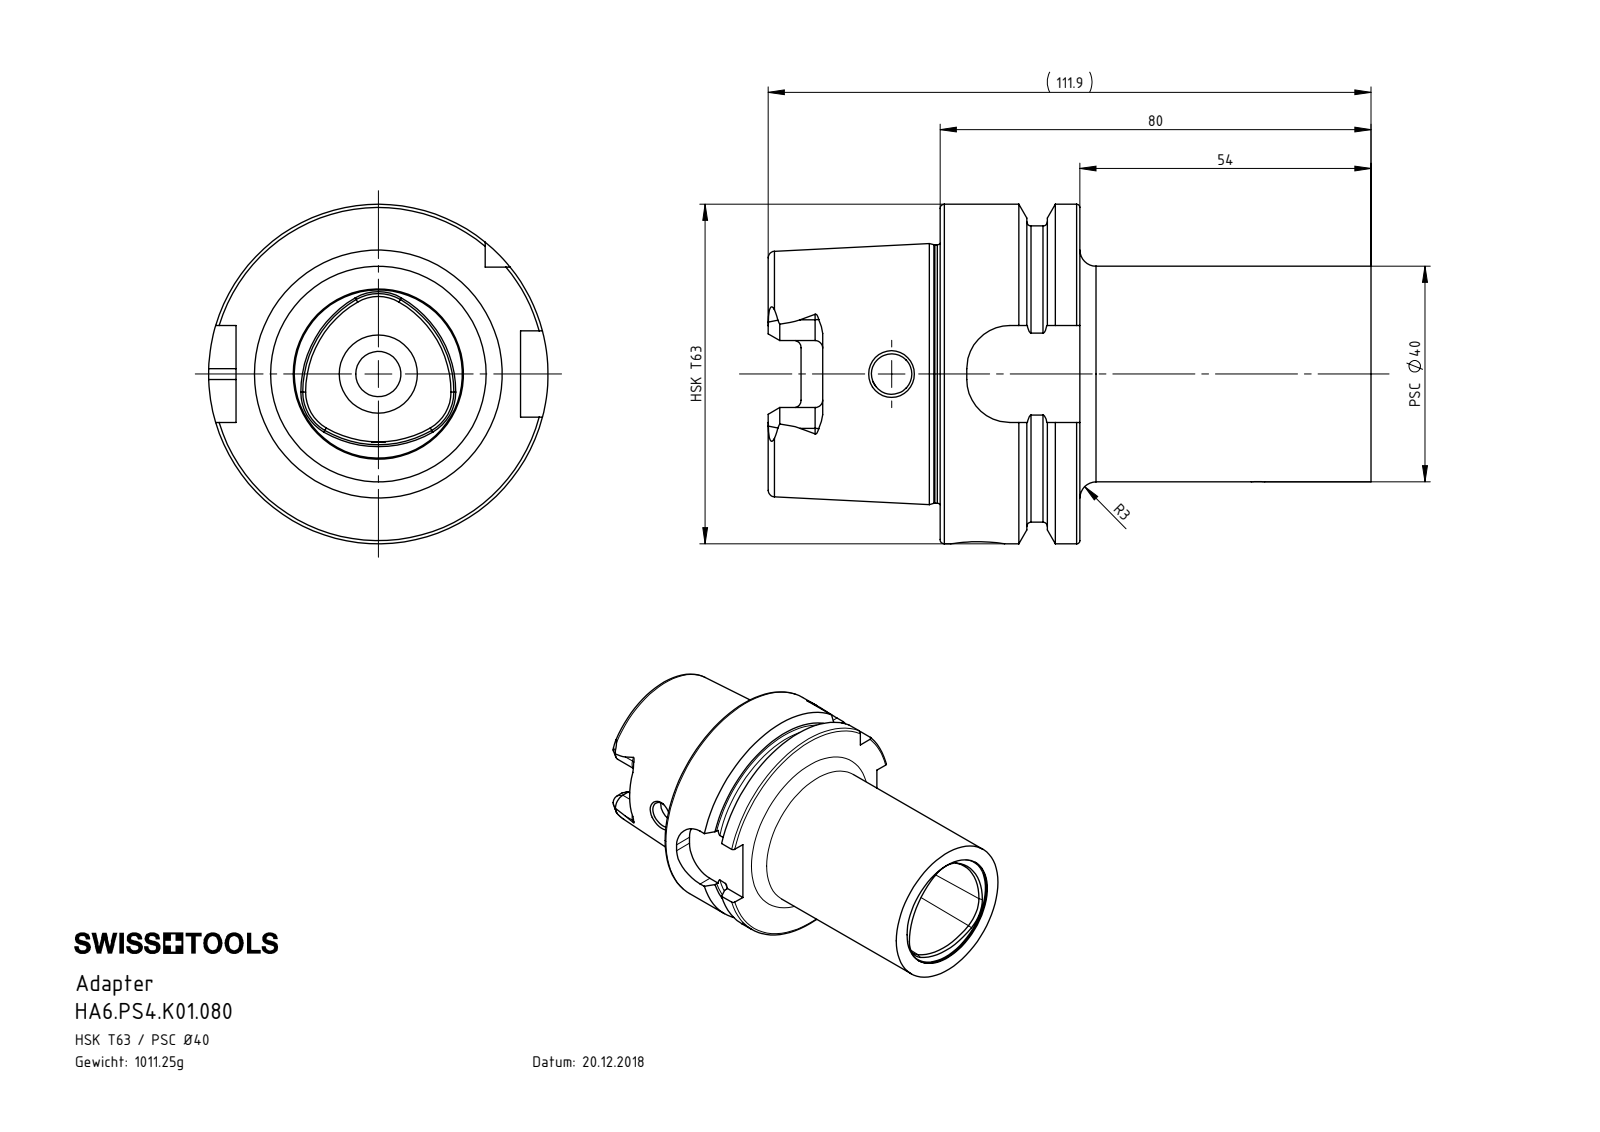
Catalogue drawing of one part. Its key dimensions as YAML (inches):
part_name: "HA6.PS4.K01.080"
step_written_by: "SolidWorks 2017 (AUTOMOTIVE_DESIGN)"
units: inches
bodies: {solids: 1, faces: 160, planar: 48, cylindrical: 40, other: 72}
overall_size: [4.406, 2.48, 2.48]
volume: 7.821
surface_area: 49.98
round_holes:
  - {diameter: 0.098, count: 1}
  - {diameter: 0.295, count: 1}
  - {diameter: 0.331, count: 1}
  - {diameter: 0.394, count: 1}
  - {diameter: 0.571, count: 1}
  - {diameter: 0.669, count: 1}
  - {diameter: 0.748, count: 1}
  - {diameter: 1.244, count: 1}
  - {diameter: 1.339, count: 1}
  - {diameter: 1.575, count: 1}
round_bosses_or_shafts:
  - {diameter: 2.48, count: 1}
  - {diameter: 2.163, count: 1}
  - {diameter: 1.887, count: 1}
partial_cylinders:
  - {radius: 0.055, count: 6}
  - {radius: 0.113, count: 4}
  - {radius: 0.315, count: 4}
  - {radius: 0.313, count: 3}
  - {radius: 0.771, count: 3}
face_to_face_distances: [1.022, 0.63, 0.392, 3.15, 2.758, 2.128, 2.035, 1.644, 1.014, 1.114]
hole_center_spacings: [2.047]
